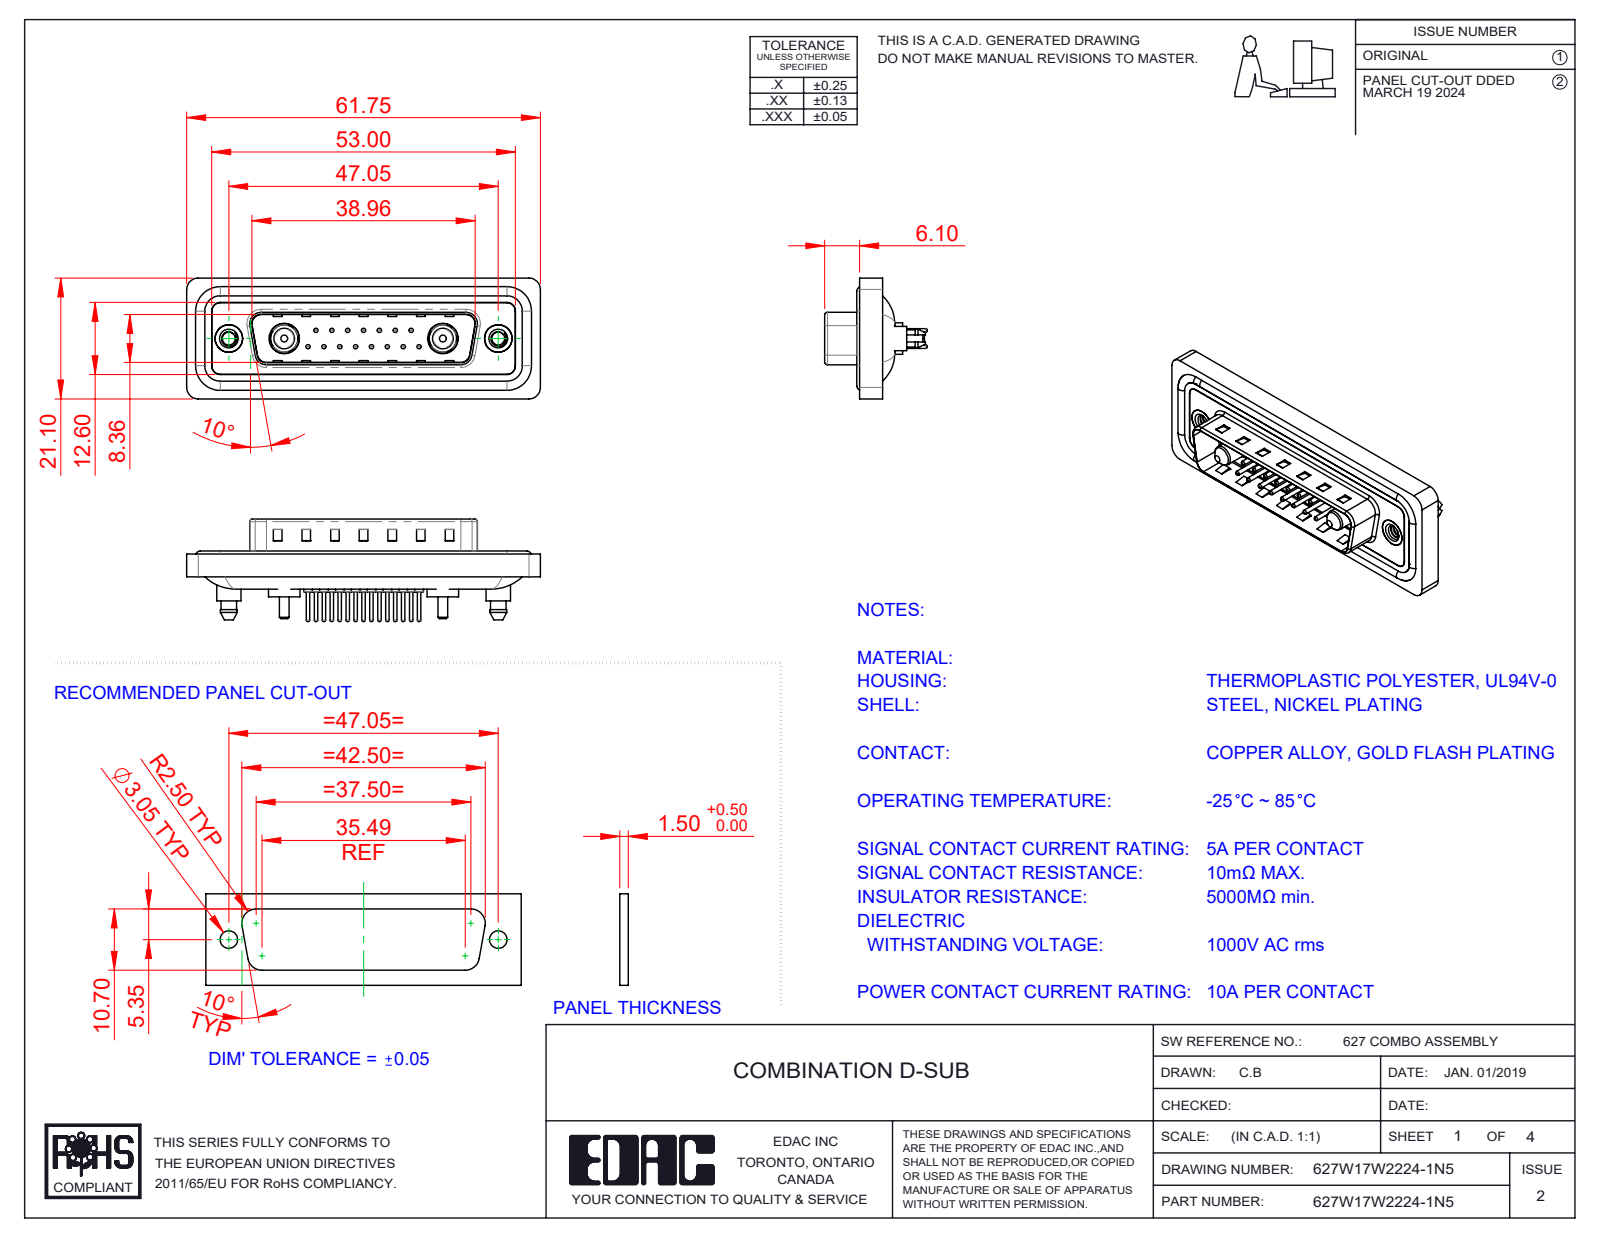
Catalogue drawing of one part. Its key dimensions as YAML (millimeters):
part_name: "627Combo Housing_17W2; 627Combo Shell Rear_25 Contacts; Power Pin_10A S; 627Combo Contact Row 1_24 (+5 more)"
step_written_by: "SolidWorks 2023 (CONFIG_CONTROL_DESIGN)"
units: millimeters
bodies: {solids: 26, faces: 1166, planar: 350, cylindrical: 468, other: 348}
overall_size: [61.75, 21.1, 17.9]
volume: 7371
surface_area: 12222
round_holes:
  - {diameter: 0.75, count: 15}
  - {diameter: 1.6, count: 15}
  - {diameter: 2, count: 15}
  - {diameter: 2.26, count: 2}
  - {diameter: 4, count: 2}
  - {diameter: 4.8, count: 2}
  - {diameter: 4.85, count: 2}
  - {diameter: 5, count: 2}
  - {diameter: 5.3, count: 2}
round_bosses_or_shafts:
  - {diameter: 1.5, count: 15}
  - {diameter: 0.6, count: 15}
  - {diameter: 1.6, count: 4}
  - {diameter: 5.5, count: 2}
  - {diameter: 5.4, count: 2}
  - {diameter: 5.2, count: 2}
  - {diameter: 4.9, count: 2}
  - {diameter: 4.75, count: 2}
partial_cylinders:
  - {radius: 1.5, count: 24}
  - {radius: 2, count: 18}
  - {radius: 1.6, count: 10}
  - {radius: 0.5, count: 8}
  - {radius: 0.25, count: 4}
  - {radius: 0.6, count: 4}
  - {radius: 0.65, count: 4}
  - {radius: 0.9, count: 4}
face_to_face_distances: [0.4, 1.5, 1.1, 1.6, 0.5, 3.1, 2.9, 0.82, 9.58, 4.1]
hole_center_spacings: [3.16, 2.77, 5.54, 8.31, 5.04, 7.49, 11.08, 5.03]
